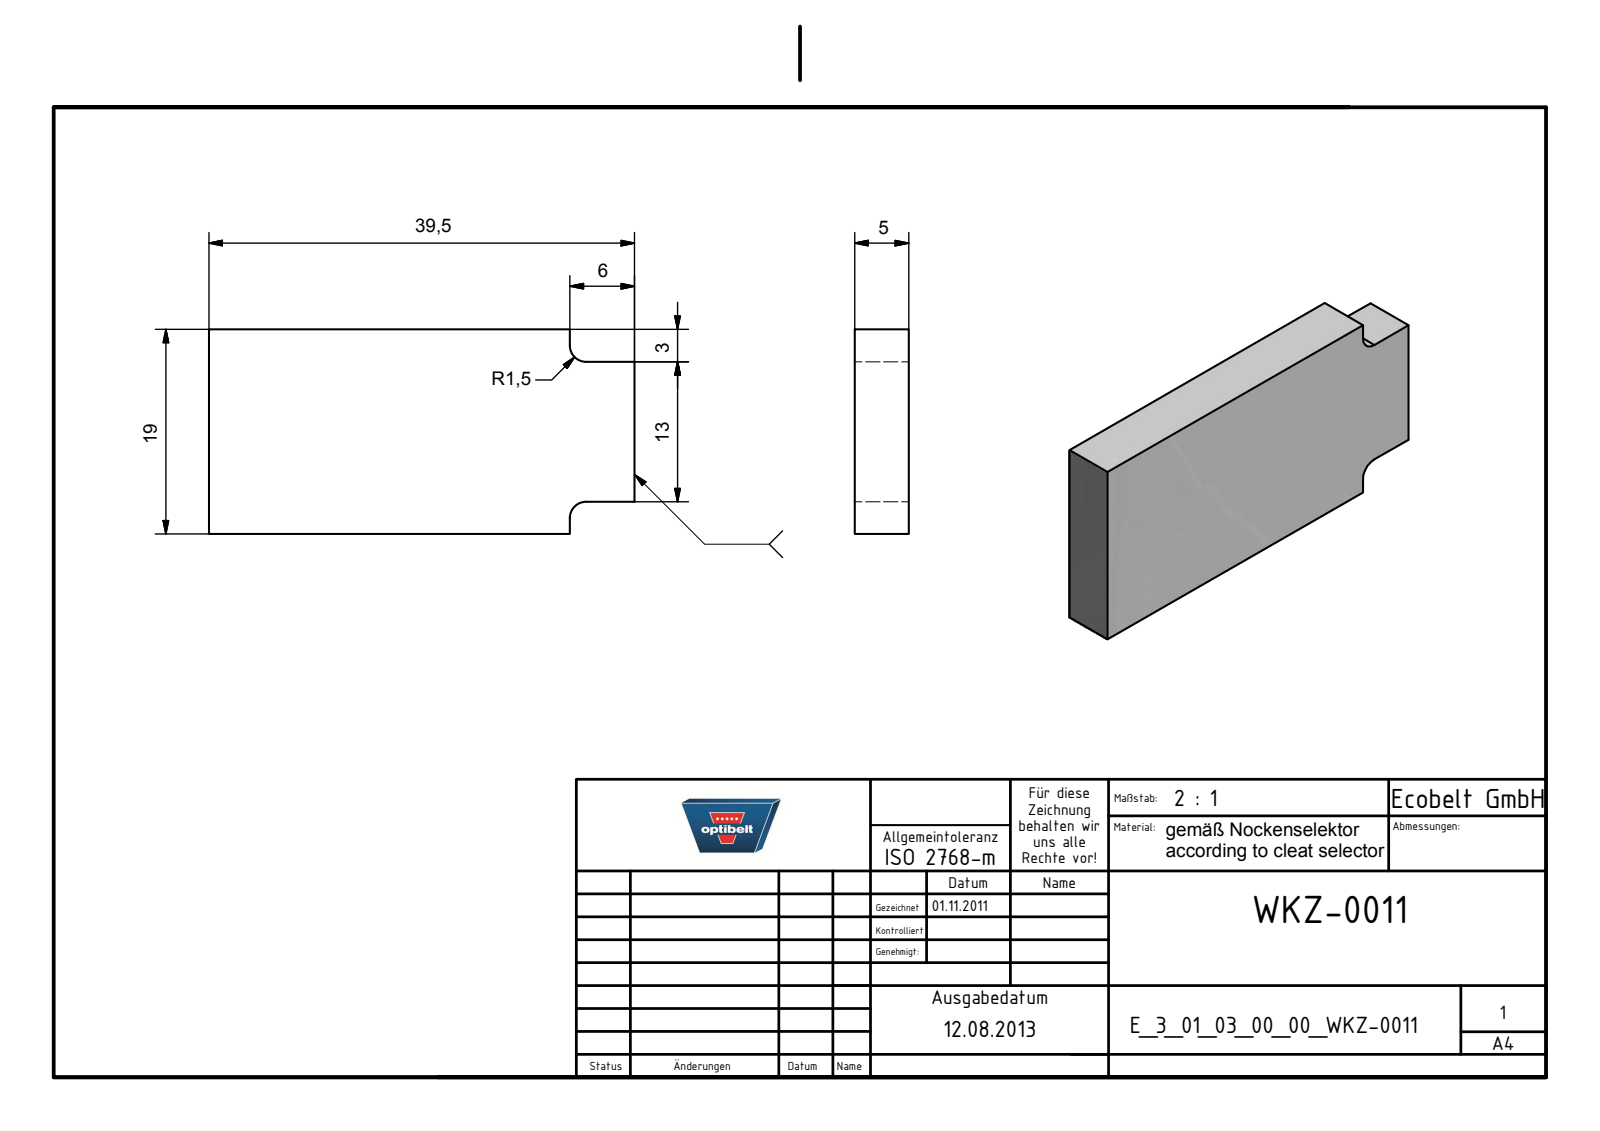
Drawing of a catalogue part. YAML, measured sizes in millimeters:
part_name: "E_3_01_03_00_00_WKZ-0011"
step_written_by: "Autodesk Inventor 2021 (AUTOMOTIVE_DESIGN)"
units: millimeters
bodies: {solids: 1, faces: 12, planar: 10, cylindrical: 2, other: 0}
overall_size: [39.5, 19, 5]
volume: 3577
surface_area: 2009
partial_cylinders:
  - {radius: 1.5, count: 2}
face_to_face_distances: [5, 19, 39.5, 3, 16, 13, 6, 33.5]
